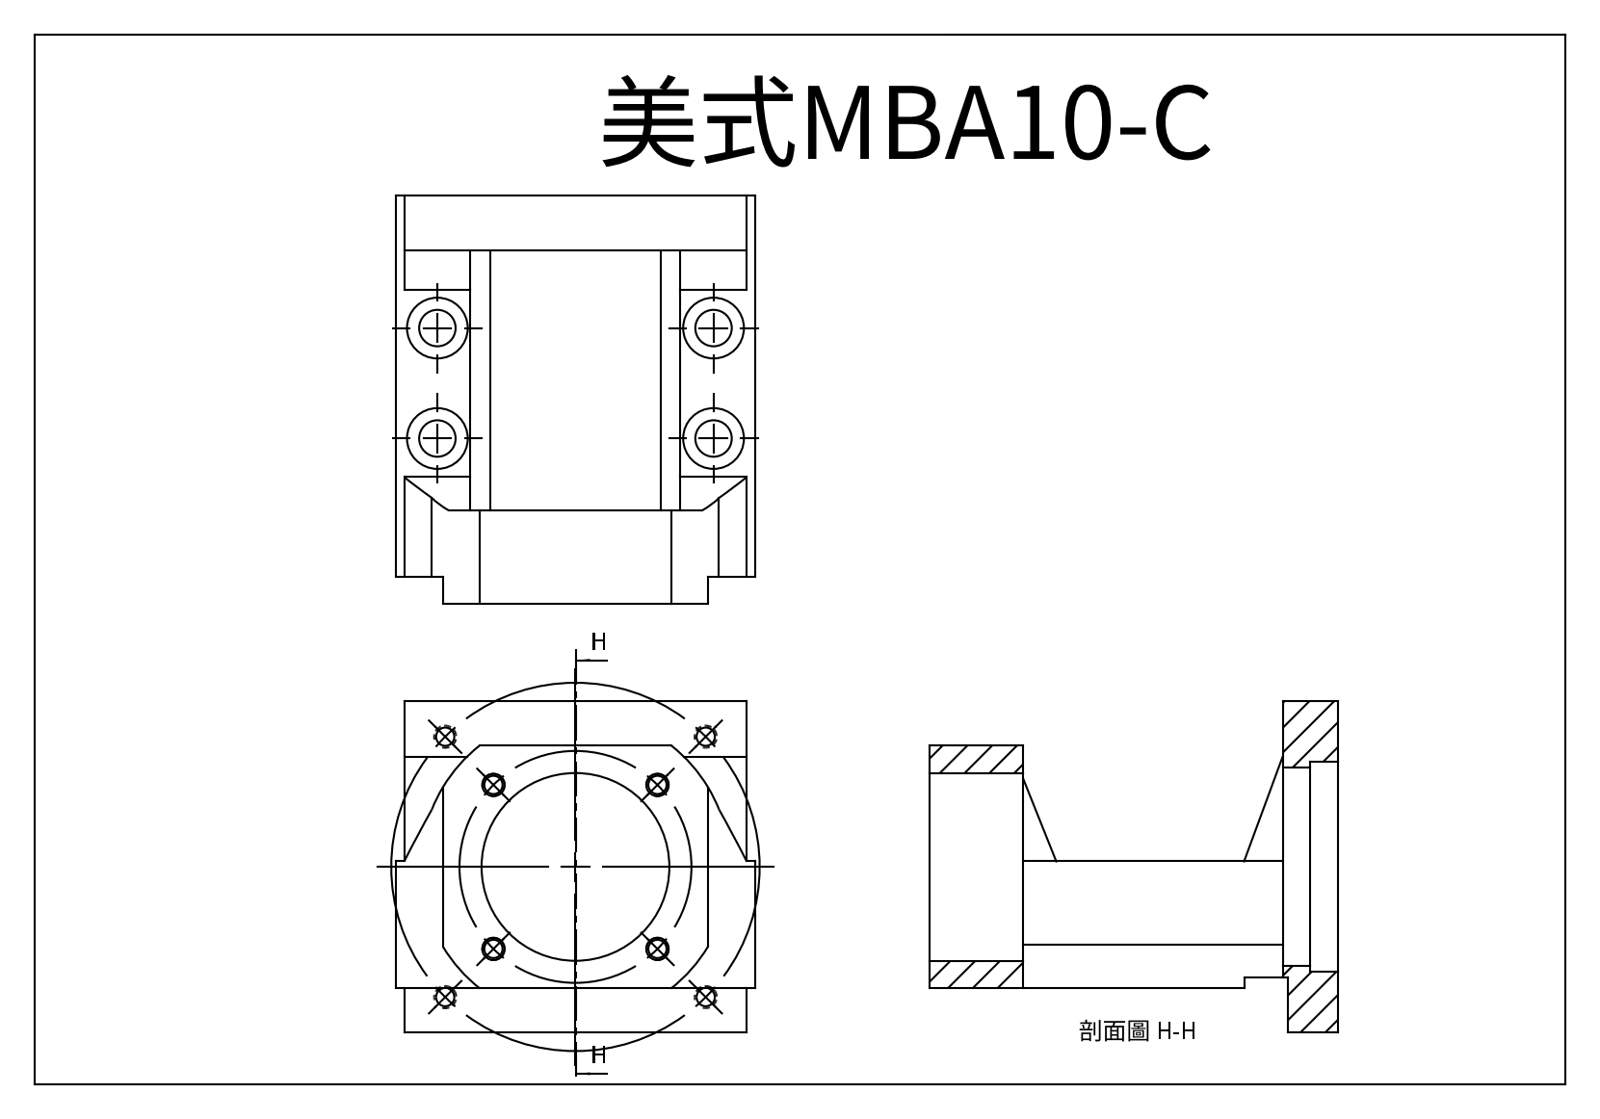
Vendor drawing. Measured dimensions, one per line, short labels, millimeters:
name: 美式MBA10-C
written by: SolidWorks 2011 (CONFIG_CONTROL_DESIGN)
unit: mm
bodies: 1 solid, 125 faces (45 planar, 52 cylindrical, 28 other)
size: 74 × 65 × 60
volume: 83 383 mm³; area: 26 413 mm²
holes: 8× ⌀3.3, 4× ⌀6.6, 4× ⌀11, 2× ⌀5.8, 2× ⌀6, 1× ⌀34, 1× ⌀36, 1× ⌀38.1
rounds: 2× R250, 1× R28
face distances: 65, 48, 17, 52, 10, 31, 60, 8, 64, 5
hole spacings: 39.41, 10, 12.35, 21, 29.7, 33.35, 47.16, 50.99
